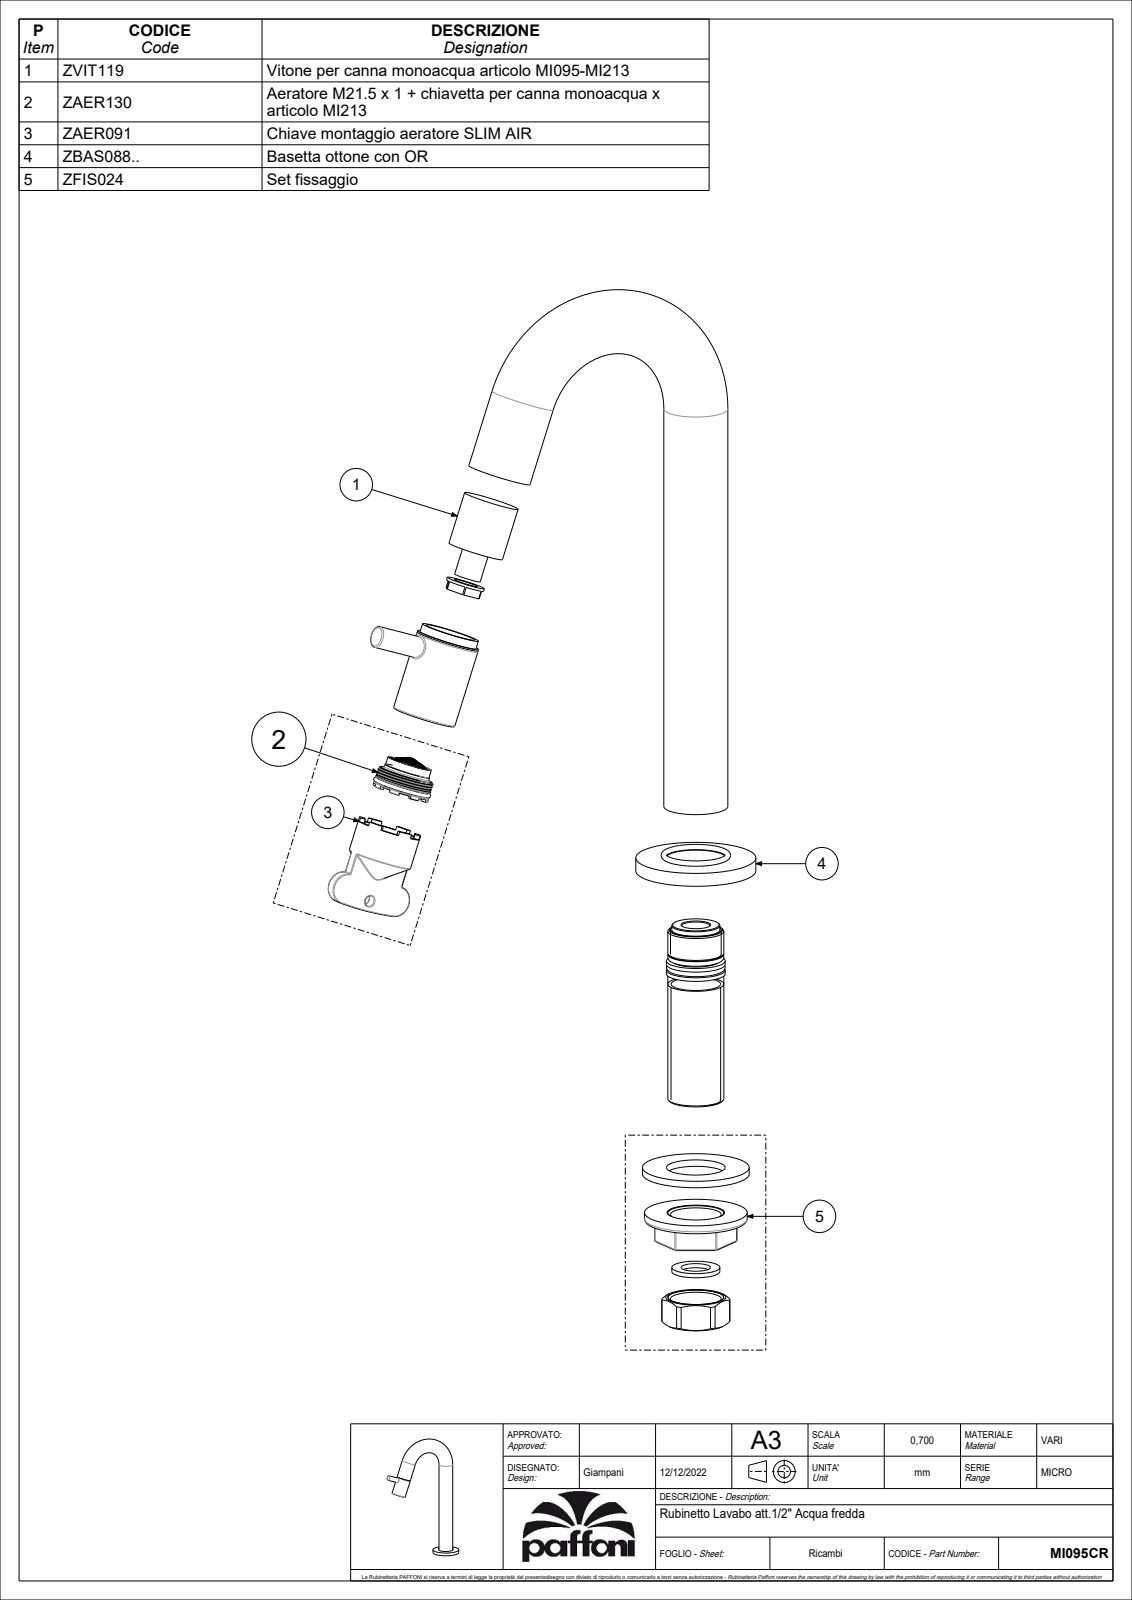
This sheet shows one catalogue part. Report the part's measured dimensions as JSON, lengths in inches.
{"part_name": "MI095CR", "step_written_by": "CREO PARAMETRIC BY PTC INC, 2020044 (CONFIG_CONTROL_DESIGN)", "units": "inches", "bodies": {"solids": 4, "faces": 3441, "planar": 2999, "cylindrical": 358, "other": 84}, "overall_size": [8.268, 5.502, 1.772], "volume_in3": 4.548, "surface_area_in2": 82.09, "round_holes": [[0.748, 3], [0.354, 2], [0.591, 2], [0.394, 1], [0.402, 1], [0.433, 1], [0.437, 1], [0.476, 1], [0.52, 1], [0.531, 1], [0.551, 1], [0.628, 1]], "round_bosses_or_shafts": [[0.031, 6], [0.945, 3], [1.772, 1], [1.063, 1], [0.941, 1], [0.866, 1], [0.843, 1], [0.758, 1]], "partial_cylinders_radius": [[0.005, 57], [0.421, 1]], "face_to_face_distances": [0.197, 0.098, 0.055, 0.067, 0.031, 0.13, 0.65, 1.2, 0.142, 0.043]}
